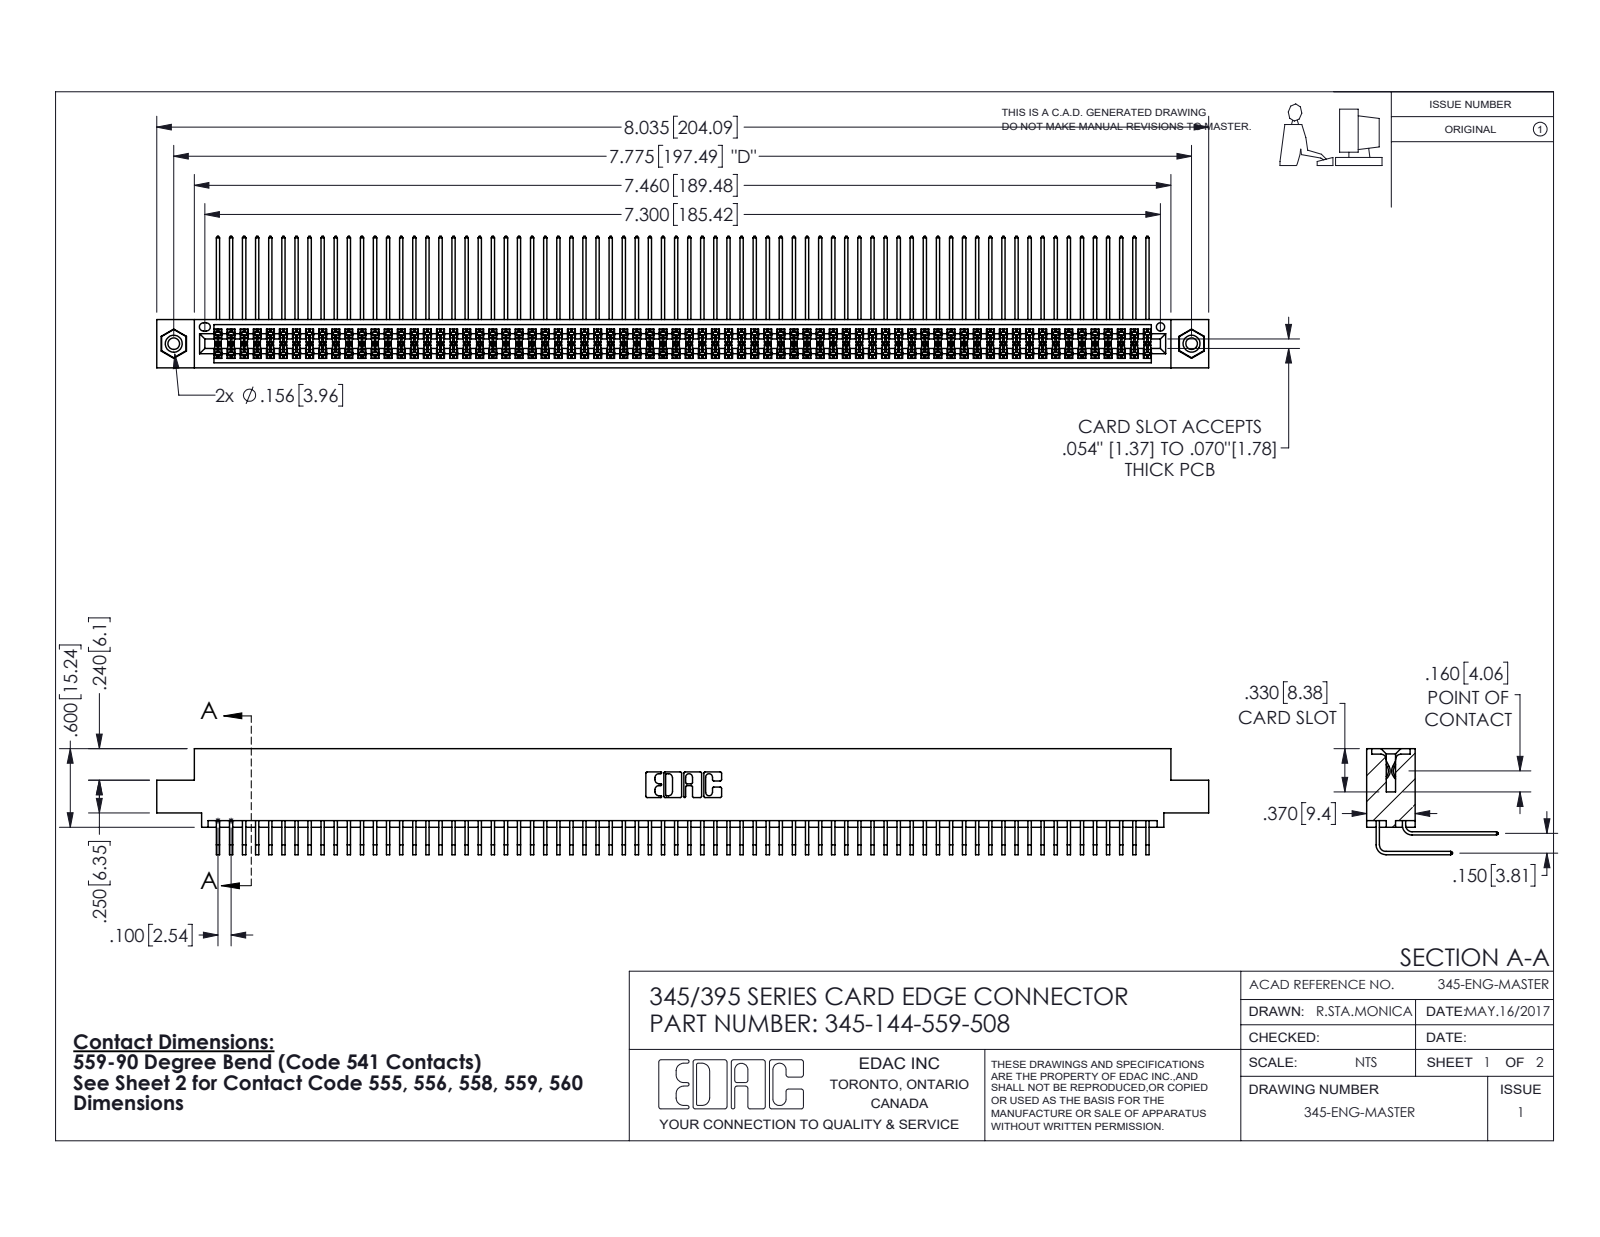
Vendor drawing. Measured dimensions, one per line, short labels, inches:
name: 345-292-001_558 559 Tail - 1; 345 Part_0.110 Offset - 0.156 Dia-TI; 345-250-001_345-250-003-102; 345-292-001_559 Tail - 2 (+1 more)
written by: SolidWorks 2016 (CONFIG_CONTROL_DESIGN)
unit: in
bodies: 147 solids, 7678 faces (5156 planar, 2506 cylindrical, 16 other)
size: 8.035 × 1.005 × 0.809
volume: 1.273 in³; area: 54.9 in²
holes: 2× ⌀0.089, 2× ⌀0.125, 2× ⌀0.156, 1× ⌀0.064
bosses: 2× ⌀0.155
rounds: 216× R0.006, 22× R0.01, 6× R0.007, 6× R0.031, 3× R0.026, 2× R0.014, 2× R0.019, 2× R0.022
face distances: 0.072, 0.298, 0.2, 0.37, 0.098, 0.272, 0.025, 0.225, 0.175, 0.15
hole spacings: 0.27, 7.539, 7.775
